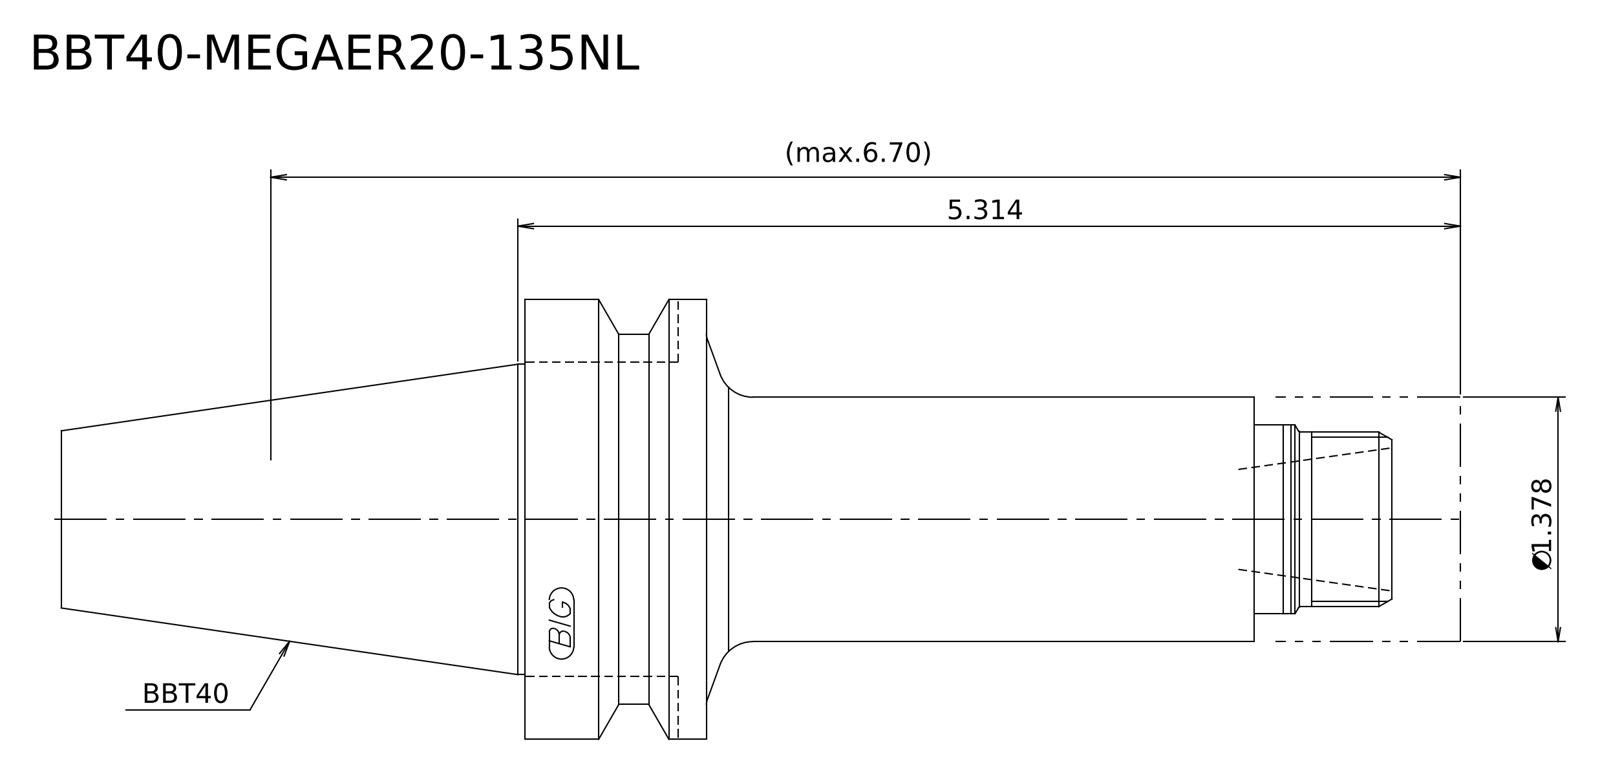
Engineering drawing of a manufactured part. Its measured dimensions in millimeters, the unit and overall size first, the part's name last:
Units: millimetres
Overall size (bounding box): 200.4 × 63 × 63
Round bosses / shafts (diameter × count): ⌀63 ×1, ⌀53 ×1, ⌀44.45 ×1, ⌀35 ×1, ⌀27 ×1, ⌀25 ×1
Main face-to-face distances: 107.5, 26.5, 134, 108, 81.5, 26, 200.4, 173.9, 92.4, 66.4
Volume: 255 142 mm³ · Surface area: 33 073 mm²
Bodies: 2 solids, 21 faces (7 planar, 8 cylindrical, 6 other)
STEP written by: Kubotek KeyCreator 2011 V10.0.2 (22737) (automotive_design)
